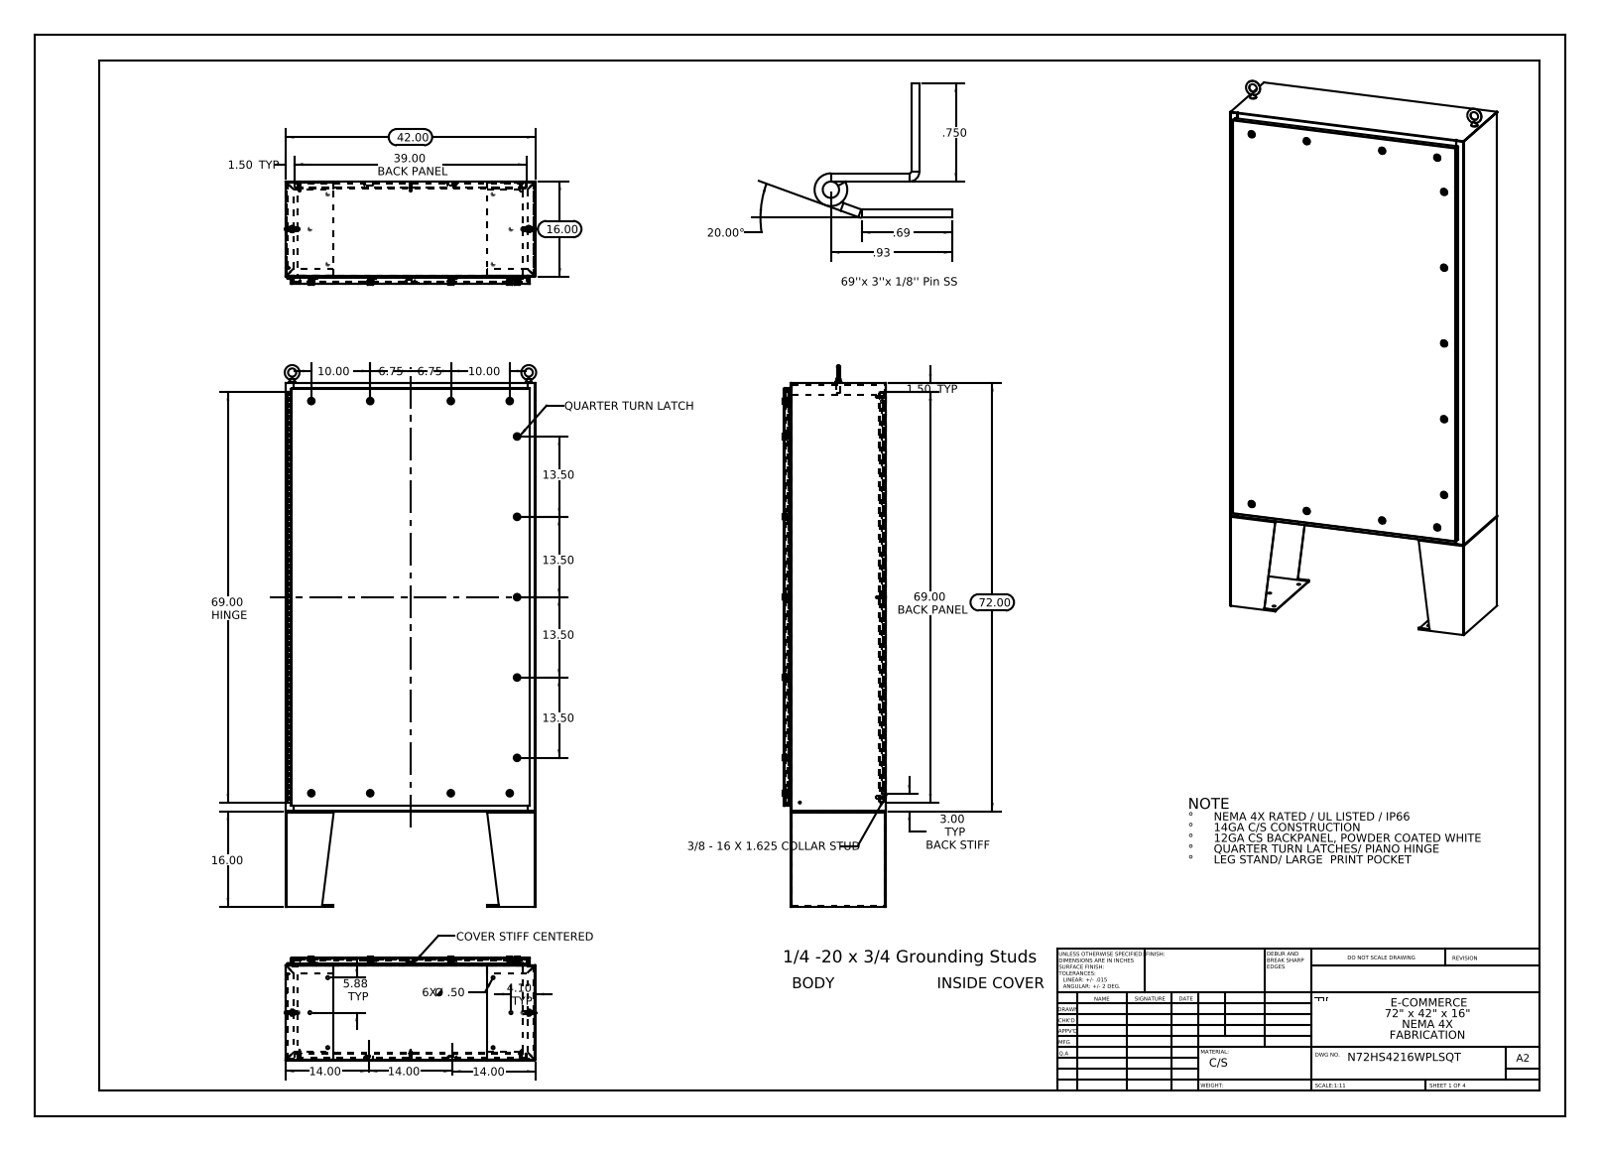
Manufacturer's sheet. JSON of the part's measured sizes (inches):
{"part_name": "Quarter-20 CD Stud; N72HS4216SSWPLSQT Mounting Studs; 10_30 CD Stud; N72HS4216SSWPLSQT Top (+8 more)", "step_written_by": "SolidWorks 2013 (CONFIG_CONTROL_DESIGN)", "units": "inches", "bodies": {"solids": 36, "faces": 2647, "planar": 1331, "cylindrical": 1120, "other": 196}, "overall_size": [91, 42.271, 17.201], "volume_in3": 1273, "surface_area_in2": 30814, "round_holes": [[0.5, 14], [0.25, 8], [0.75, 4], [0.125, 1], [0.125, 1]], "round_bosses_or_shafts": [[0.625, 10], [0.375, 8], [0.33, 8], [0.157, 8], [0.14, 8], [0.315, 2], [0.236, 2], [0.25, 1]], "partial_cylinders_radius": [[0.013, 36], [0.088, 30], [0.039, 8], [0.143, 8], [0.442, 8], [0.019, 6], [0.117, 4], [0.125, 4]], "face_to_face_distances": [0.075, 17.126, 0.104, 17.051, 1.075, 17.201, 16.126, 1, 16.051, 1.179], "hole_center_spacings": [2.225, 8.393, 31.348, 33.625, 34.289, 38.439, 50.181, 69.781]}
